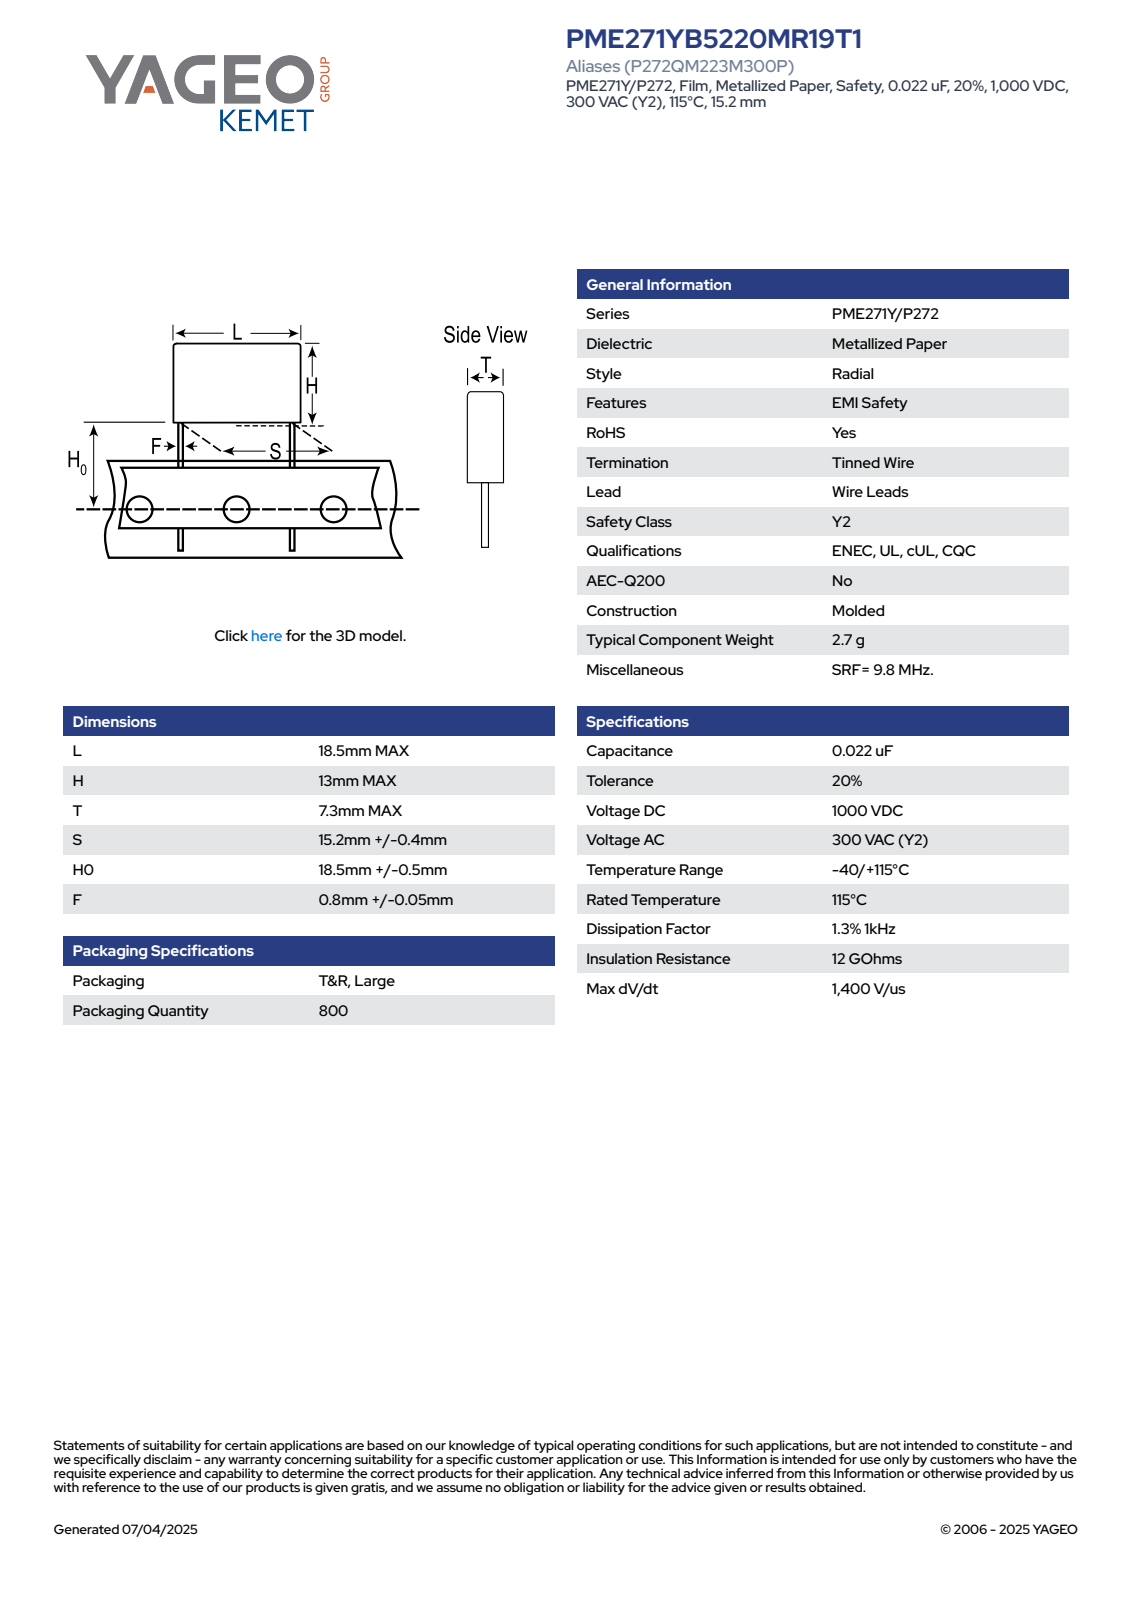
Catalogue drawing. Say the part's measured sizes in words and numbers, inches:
The part is named "CFR_MOLDED_18.5X13X7.3_L18.5H13T7.3S15.2H019F0.85". Its 3-D file was written by "SolidWorks 2014 (AUTOMOTIVE_DESIGN)". It is 4 solids with 73 faces: 65 planar, 8 cylindrical and 0 other. Overall it measures 1.26 by 0.728 by 0.287 inches. Its volume is 0.108 cubic inches and its surface area 1.624 square inches. Round bosses or shafts: 2 of diameter 0.033. Partial cylindrical surfaces (rounded edges, fillets, slot ends): 4 of radius 0.02. The main face-to-face distances are 0.287, 0.512, 0.728, 0.748, 1.26, 0.065, 1.028, 0.28, 0.232, 0.963.
